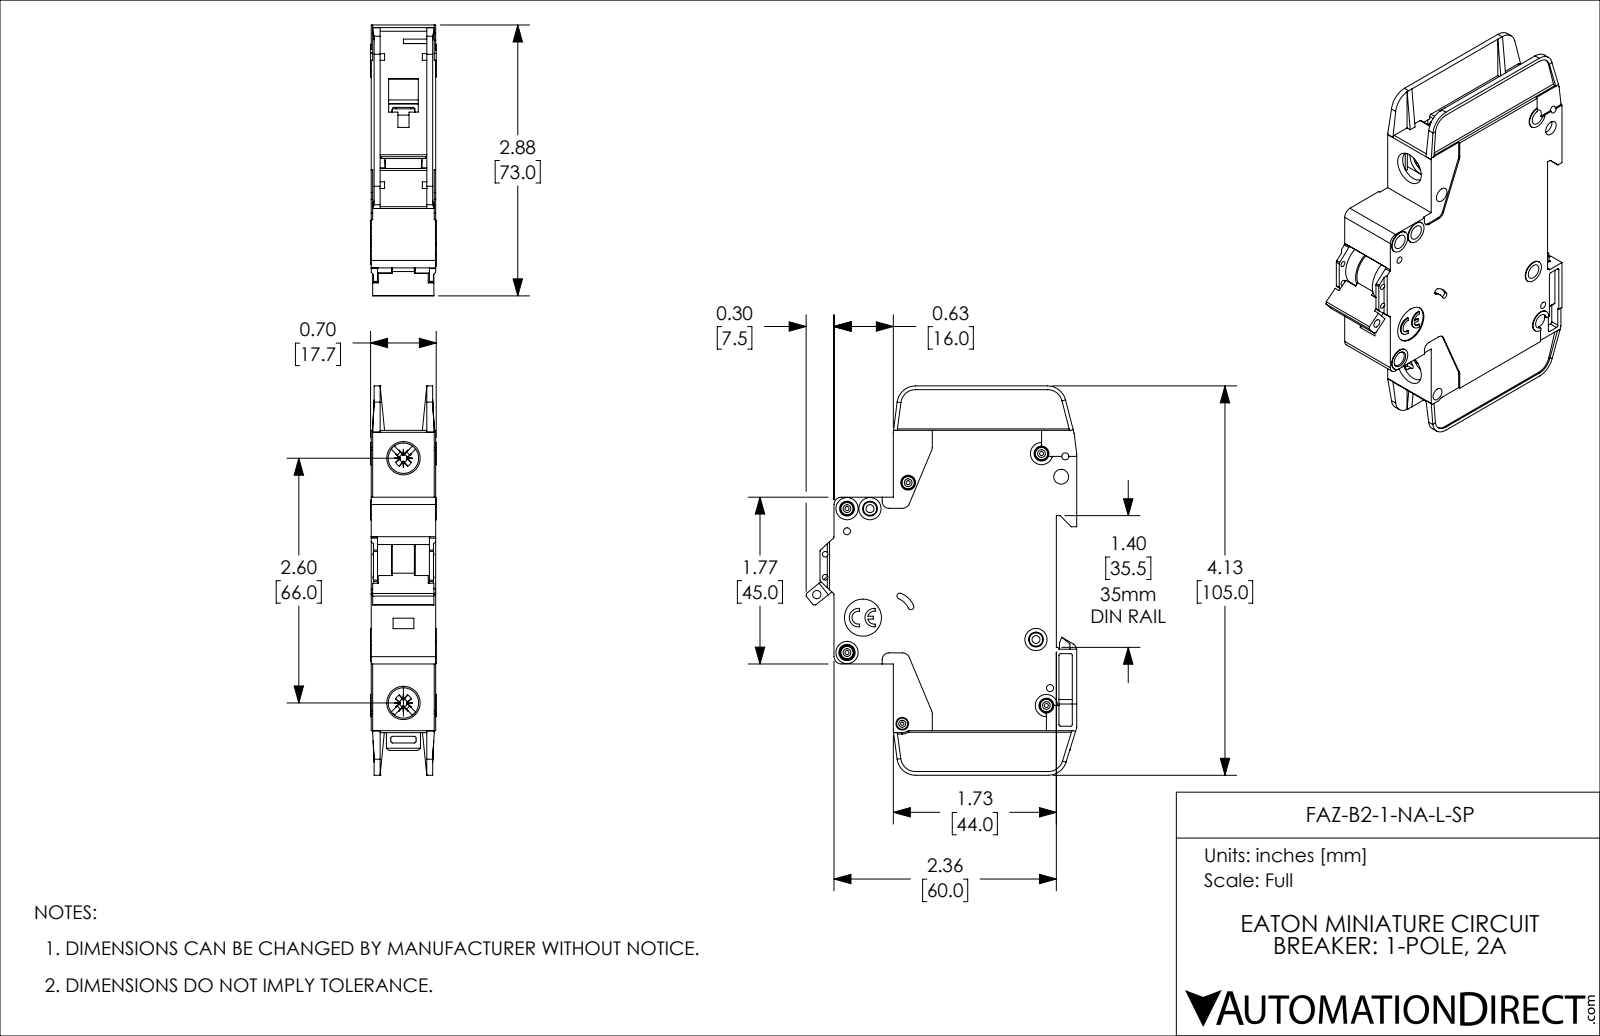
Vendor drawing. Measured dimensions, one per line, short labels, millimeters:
name: FAZ-B2-1-NA-L-SP
written by: SolidWorks 2019 (AUTOMOTIVE_DESIGN)
unit: mm
bodies: 1 solid, 1127 faces (671 planar, 357 cylindrical, 99 other)
size: 105 × 73.1 × 17.7
volume: 76 720 mm³; area: 26 460 mm²
holes: 8× ⌀4, 5× ⌀1.1, 4× ⌀1.9, 2× ⌀1.5, 2× ⌀2.2, 2× ⌀8.2, 1× ⌀0.9, 1× ⌀2.3, 1× ⌀2.5, 1× ⌀3.4, 1× ⌀10
bosses: 5× ⌀3.3, 4× ⌀6, 2× ⌀3, 1× ⌀2.5
rounds: 42× R0.5, 10× R0.4, 10× R1, 8× R2, 5× R5, 4× R0.2, 4× R0.7, 4× R1.1
face distances: 1.2, 17.4, 15, 16.2, 2.4, 13.8, 0.4, 0.8, 12.6, 14.6
hole spacings: 6.2, 13.6, 22.1, 4.8, 5.1, 5.2, 5.6, 6.1
